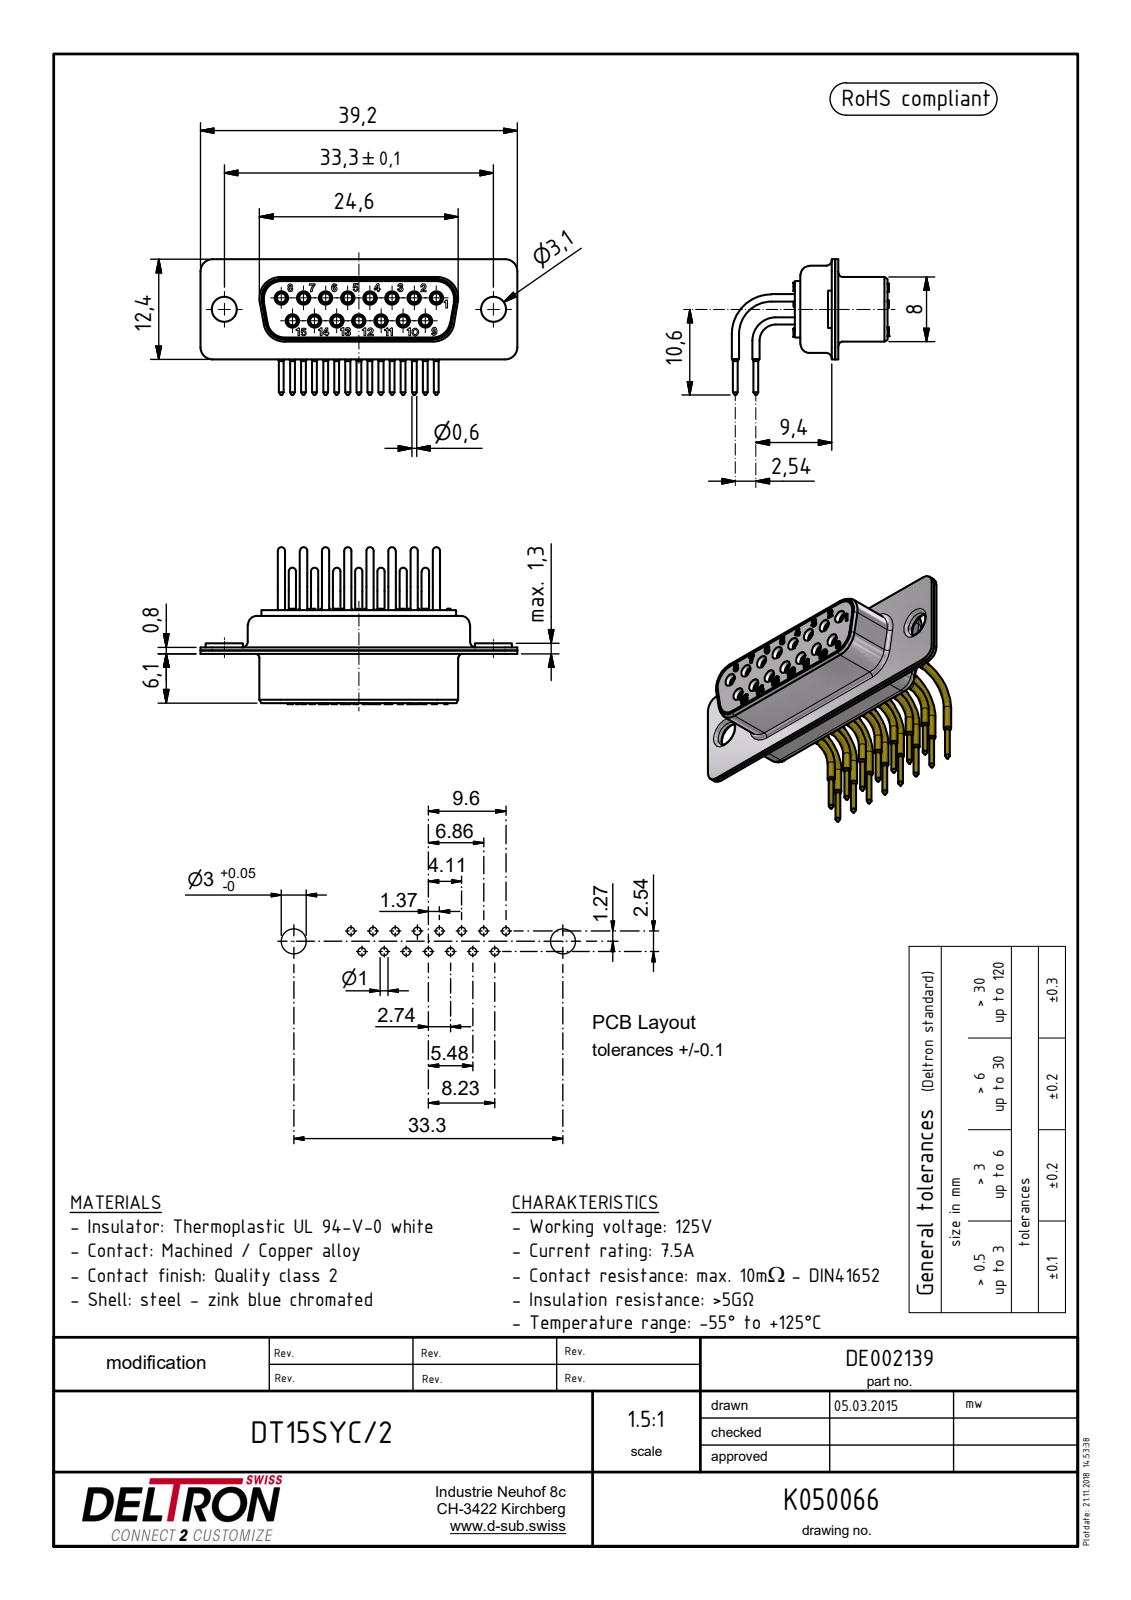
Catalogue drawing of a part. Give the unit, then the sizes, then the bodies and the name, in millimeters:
Units: millimetres
Overall size (bounding box): 39.2 × 19.44 × 16.8
Round holes (diameter × count): ⌀1.15 ×15, ⌀1.92 ×15, ⌀2.3 ×15, ⌀0.34 ×4, ⌀0.24 ×2, ⌀0.28 ×2, ⌀3.1 ×2, ⌀4.06 ×2
Round bosses / shafts (diameter × count): ⌀0.9 ×30, ⌀1.96 ×15, ⌀1.7 ×15, ⌀1.6 ×15, ⌀0.6 ×15, ⌀4.6 ×2, ⌀3.9 ×2
Partial cylindrical surfaces — rounded edges, fillets, slot ends (radius × count): R0.25 ×16, R1.07 ×15, R2 ×12, R0.7 ×8, R1.1 ×8, R2.2 ×8, R0.34 ×4, R0.5 ×4
Main face-to-face distances: 0.4, 0.8, 0.5, 1.4, 10.2, 7.1, 7.6, 7.5, 1.3, 9
Hole centre spacings: 3.15, 2.74, 5, 5.48, 7.42, 8.22, 10, 10.96
Volume: 2 418 mm³ · Surface area: 6 553 mm²
Bodies: 18 solids, 2875 faces (1714 planar, 854 cylindrical, 307 other)
Part name (STEP PRODUCT): N00404_BG; R+B00918_BG; R+B00917_BG; R+B00153_BG (+2 more)
STEP written by: Autodesk Inventor 2015 (AUTOMOTIVE_DESIGN)
